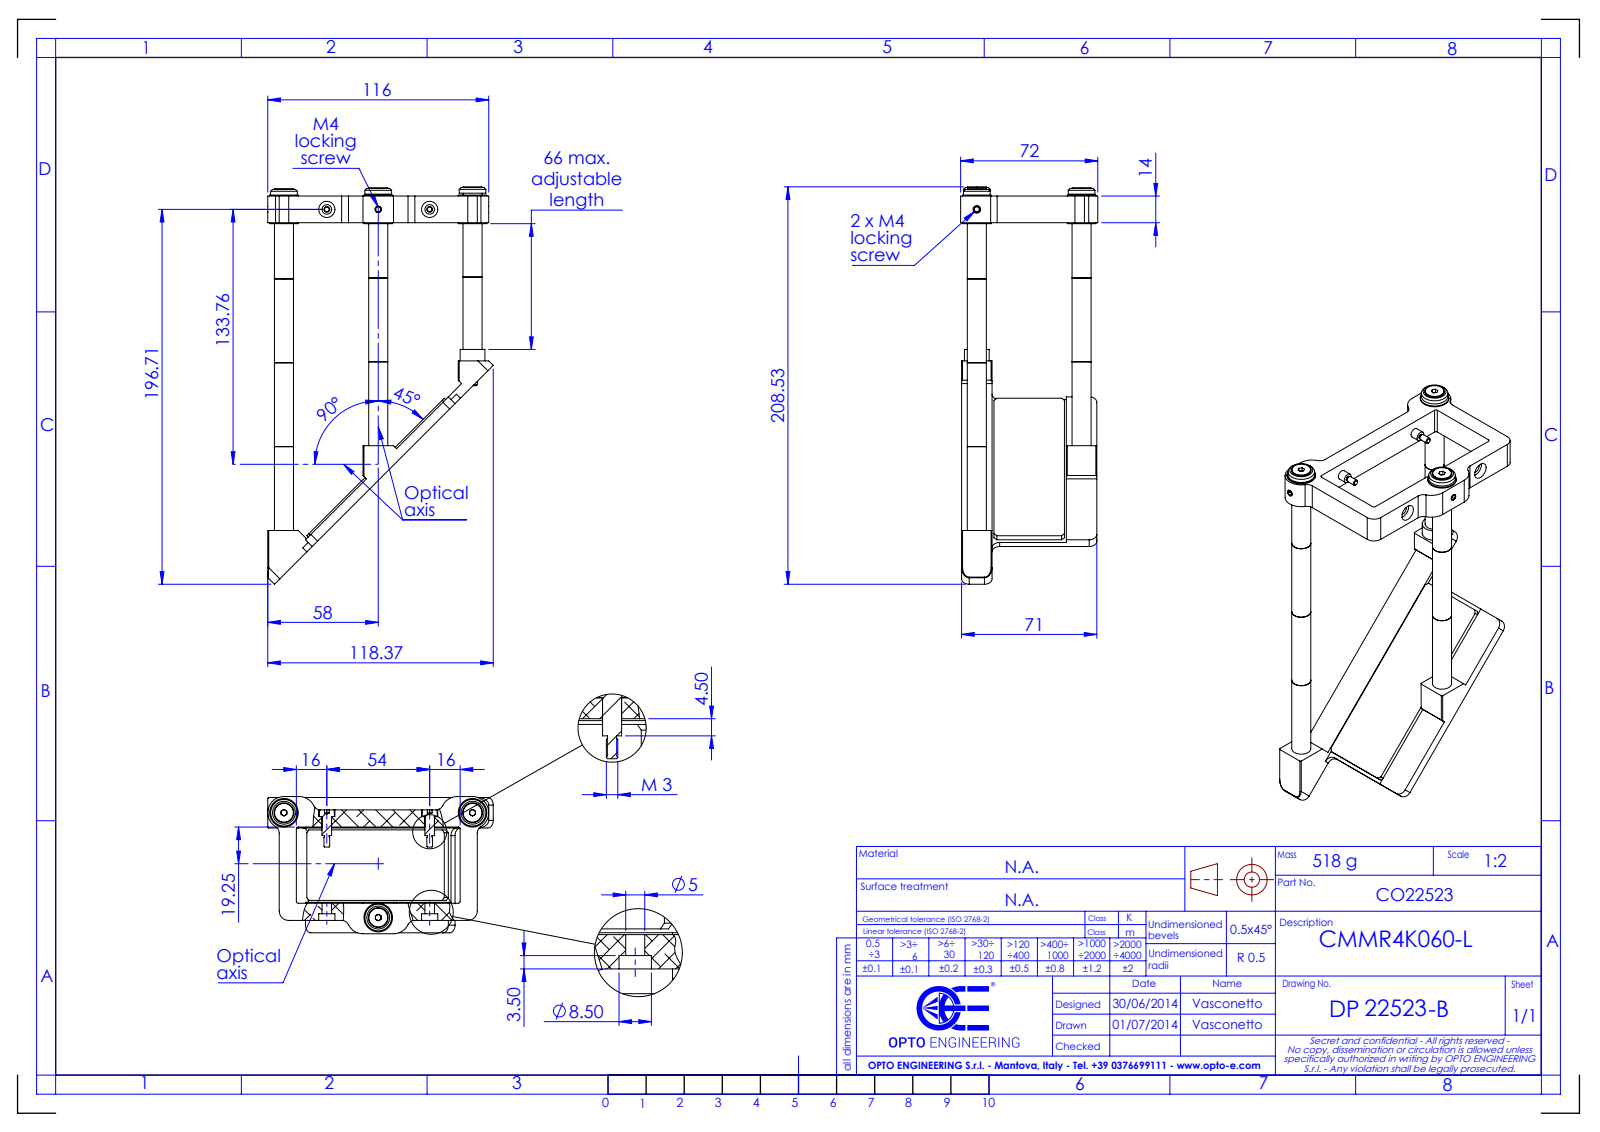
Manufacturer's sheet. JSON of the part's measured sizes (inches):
{"part_name": "DP22523-B_CMMR4K060-L", "step_written_by": "SolidWorks 2021 (CONFIG_CONTROL_DESIGN)", "units": "inches", "bodies": {"solids": 0, "faces": 273, "planar": 131, "cylindrical": 102, "other": 40}, "overall_size": [8.21, 4.66, 2.835], "round_holes": [[0.165, 3], [0.197, 2], [0.335, 2]], "round_bosses_or_shafts": [[0.591, 3], [0.551, 3], [0.394, 3], [0.388, 3], [0.118, 2], [0.094, 2], [0.512, 1], [0.197, 1]], "partial_cylinders_radius": [[0.157, 14], [0.335, 6], [0.039, 4], [0.197, 2]], "face_to_face_distances": [0.118, 0.236, 0.039, 0.079, 0.197, 0.551, 0.354, 0.02, 2.185, 0.61], "hole_center_spacings": [2.913, 2.126, 3.898]}
